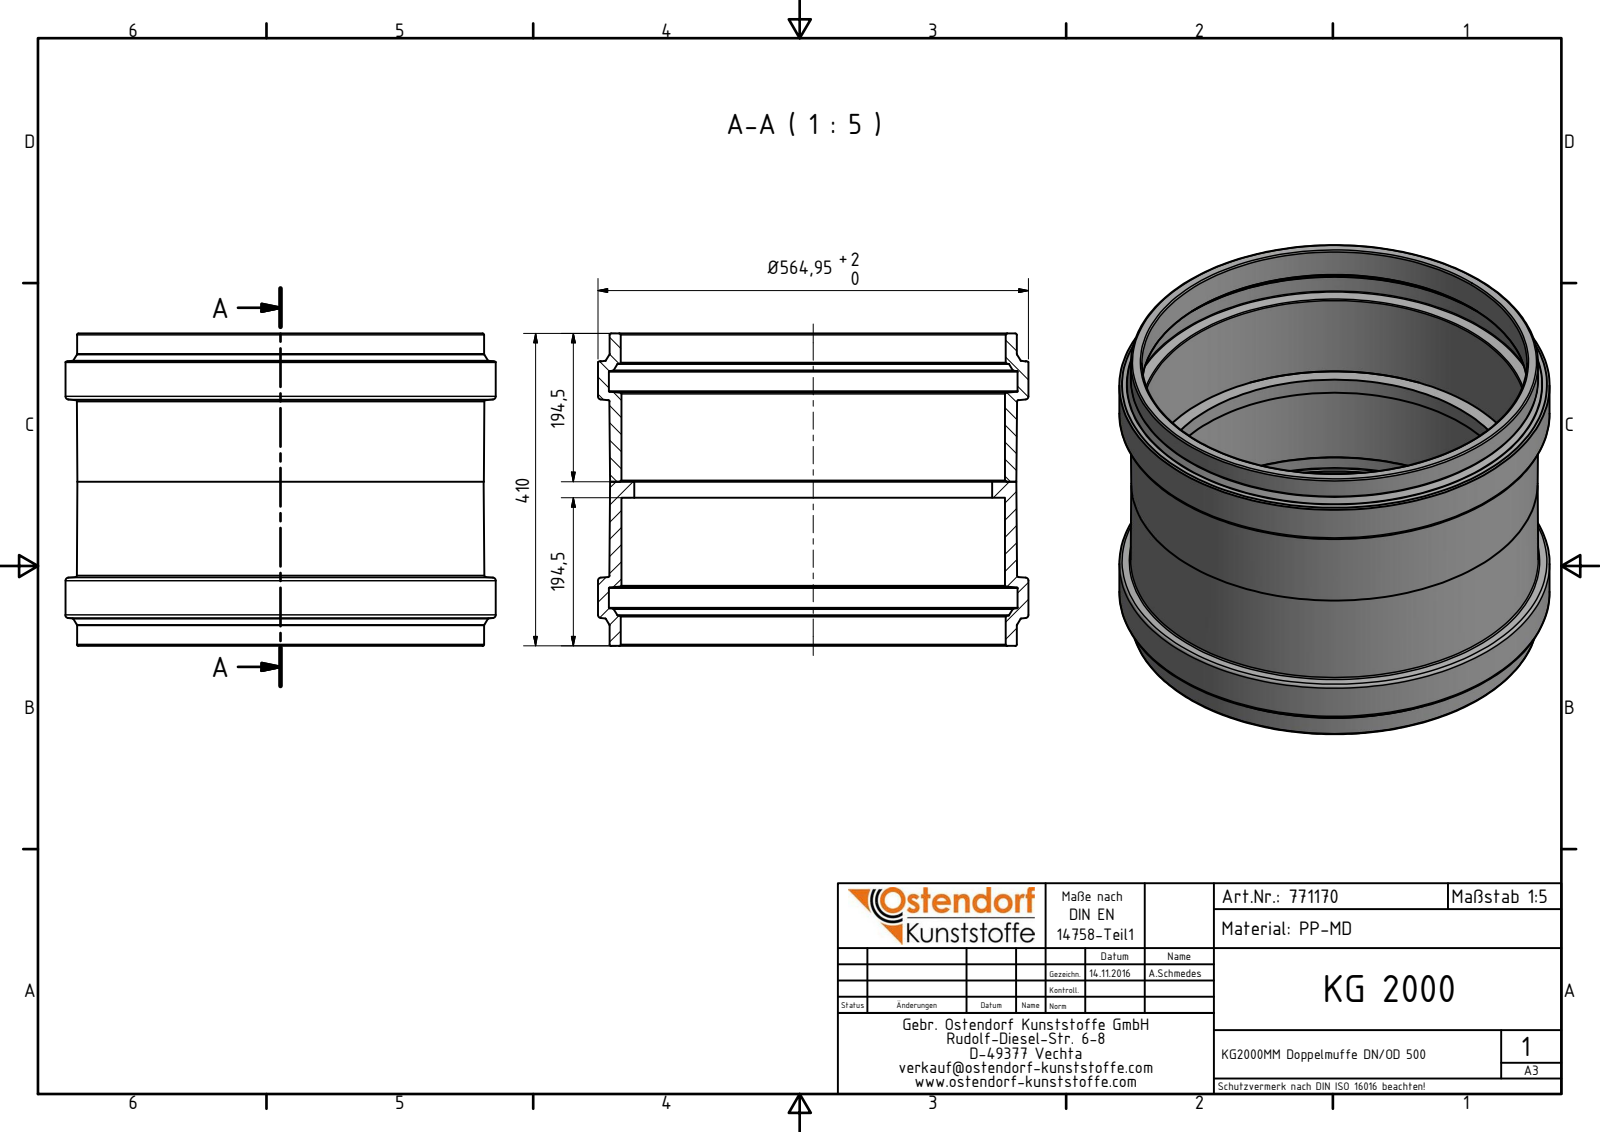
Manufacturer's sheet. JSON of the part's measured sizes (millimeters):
{"part_name": "771170 KG2000MM Doppelmuffe DN_OD 500 Teil 1; 771170 KG2000MM Doppelmuffe DN_OD 500 Teil 2; 771170 KG2000MM Doppelmuffe DN_OD 500 Zusammenbau", "step_written_by": "Autodesk Inventor 2016 (AUTOMOTIVE_DESIGN)", "units": "millimeters", "bodies": {"solids": 2, "faces": 59, "planar": 5, "cylindrical": 11, "other": 43}, "overall_size": [565, 565, 410], "volume_mm3": 11740000, "surface_area_mm2": 1643000, "round_holes": [[470.18, 1], [503.65, 1], [505.6, 1], [505.65, 1], [536.66, 1]], "round_bosses_or_shafts": [[565, 1], [564.95, 1], [534.54, 1], [534.49, 1]], "face_to_face_distances": [194.5, 215.5, 21, 410]}
